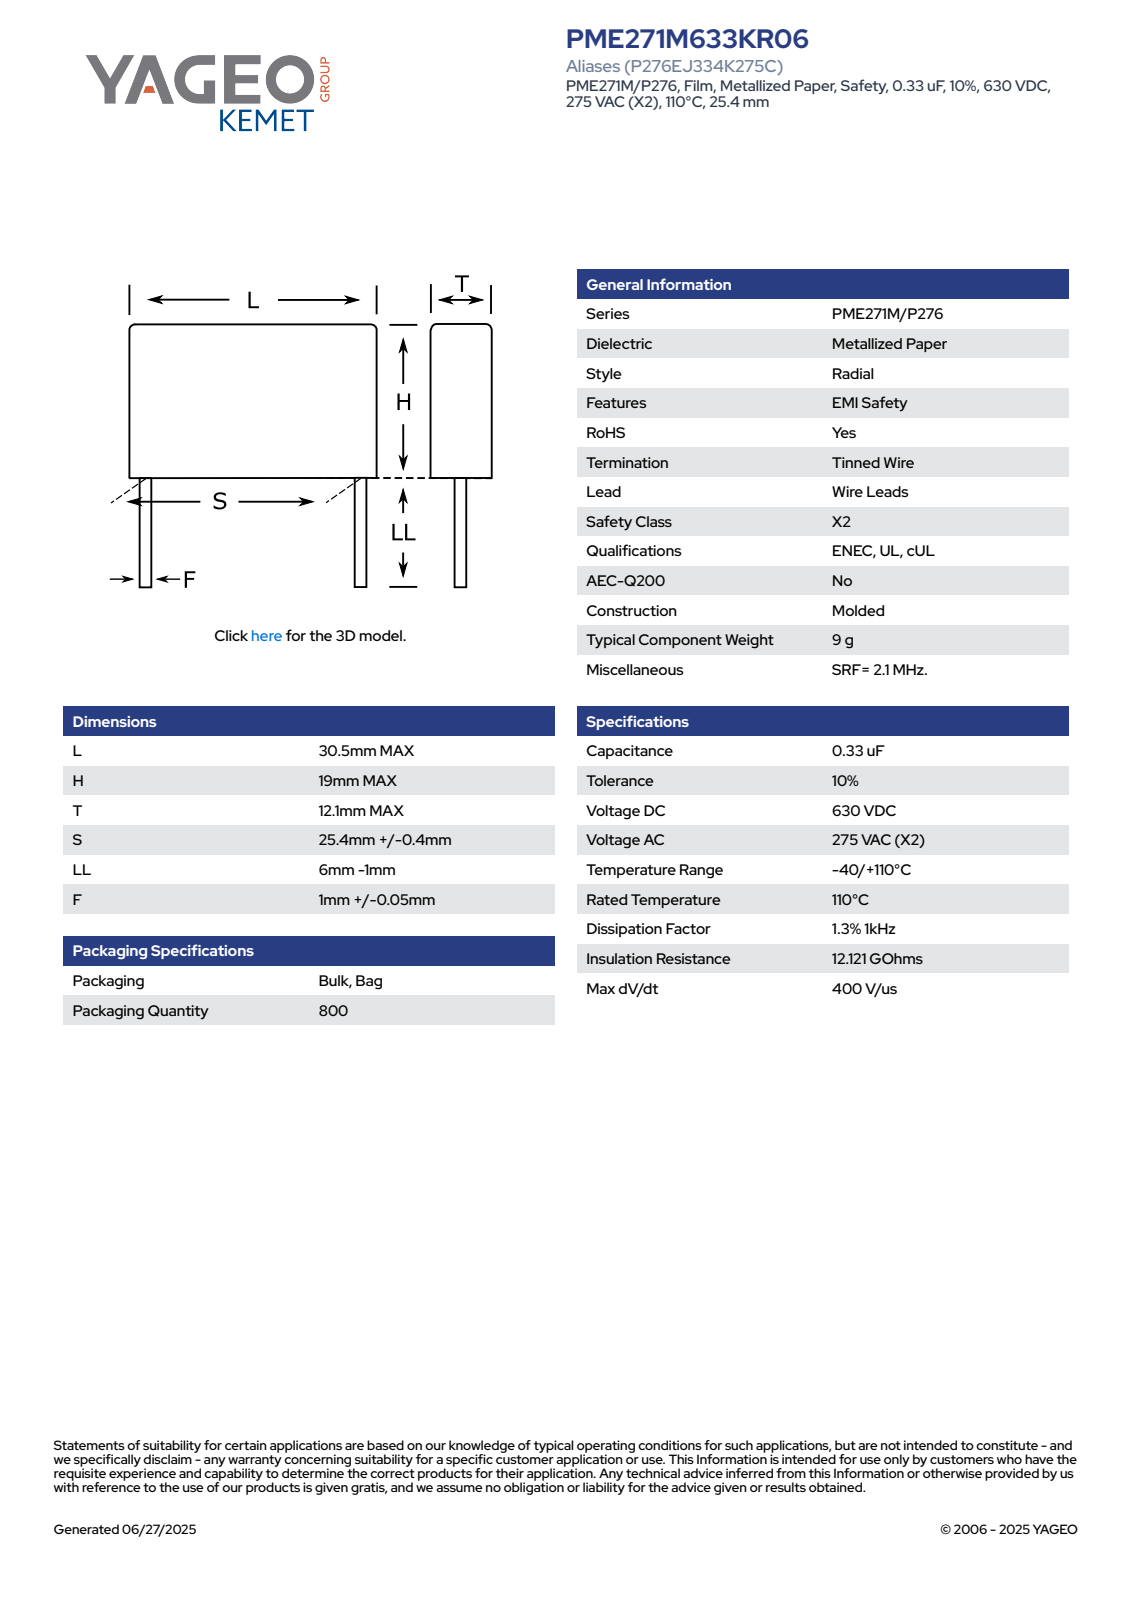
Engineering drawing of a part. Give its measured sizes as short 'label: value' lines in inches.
name: CFR_MOLDED_30.5X19X12.1_L30.5H19T12.1S25.4LL5F1.05
written by: SolidWorks 2014 (AUTOMOTIVE_DESIGN)
unit: in
bodies: 4 solids, 73 faces (65 planar, 8 cylindrical, 0 other)
size: 1.201 × 0.945 × 0.477
volume: 0.428 in³; area: 3.745 in²
bosses: 2× ⌀0.041
rounds: 4× R0.02
face distances: 0.476, 0.748, 1.201, 0.197, 0.945, 0.618, 0.421, 0.327, 0.511, 0.314
